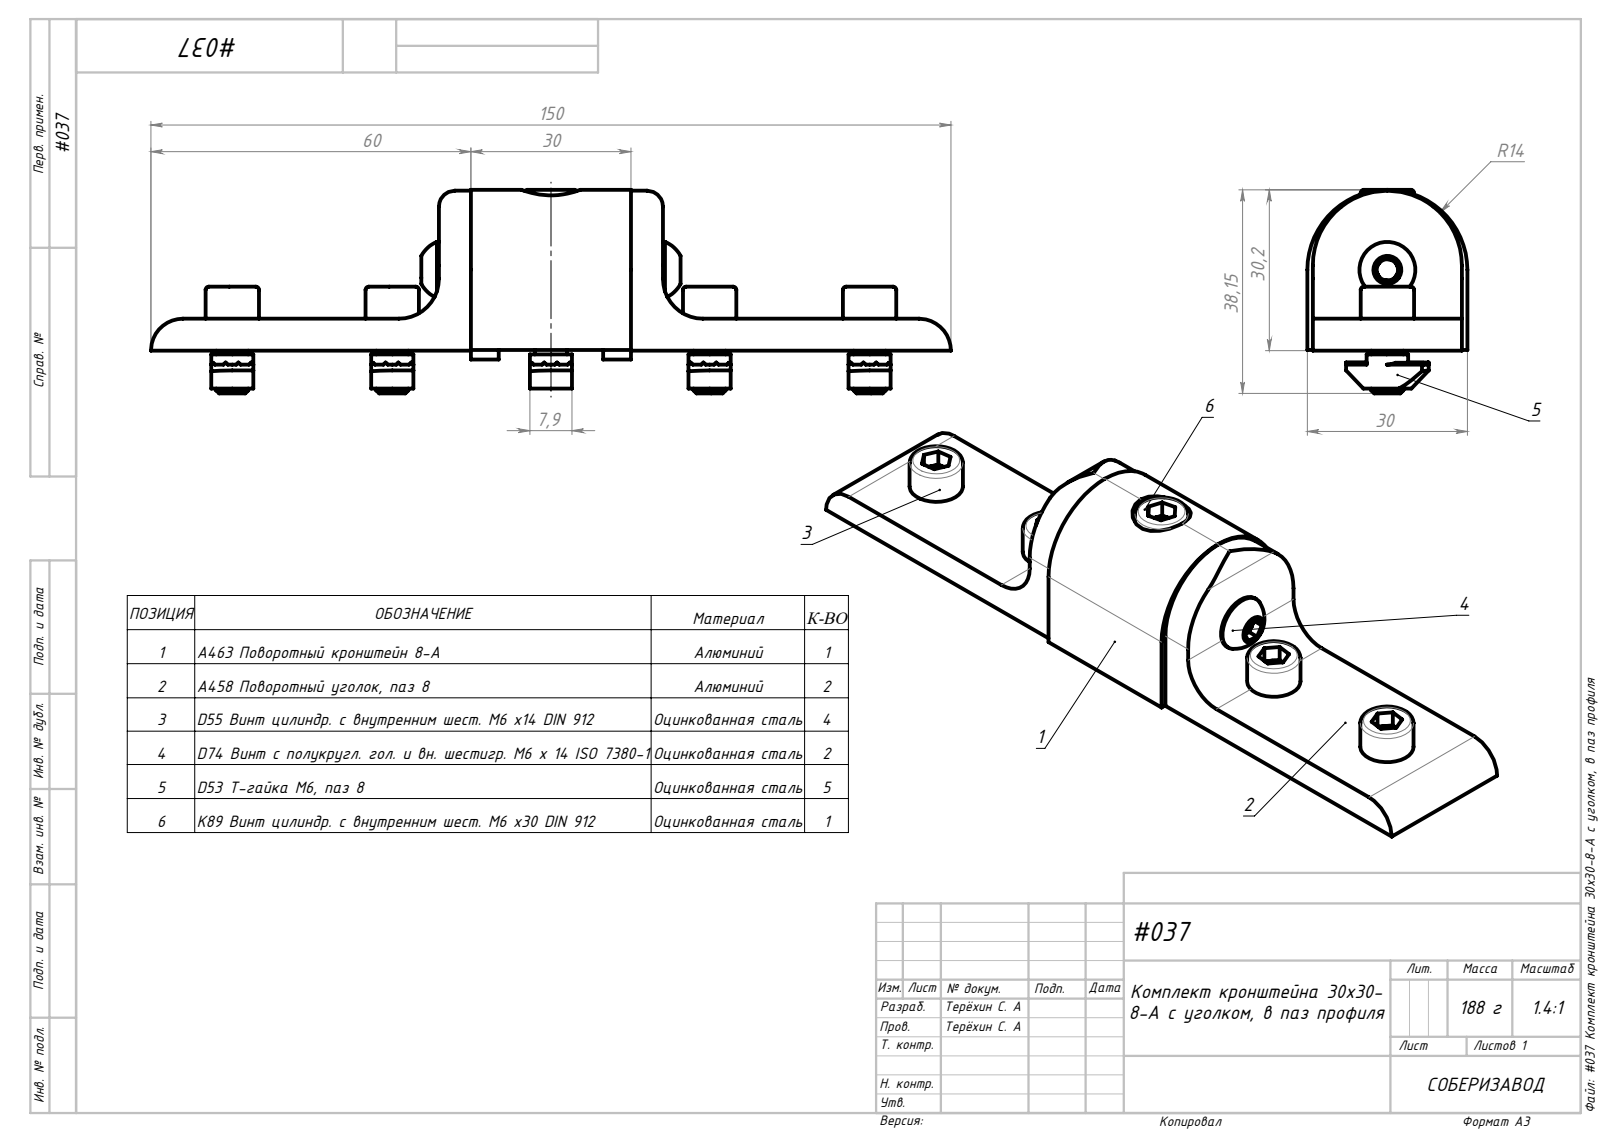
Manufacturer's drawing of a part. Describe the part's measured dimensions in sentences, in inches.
The part is named "A463 Поворотный кронштейн 8-A; #037 Комплект кронштейна 30х30-8-А с уголком, в паз профиля; D74 Винт с полукругл. гол. и вн. шестигр. М6 х 14 ISO 7380-1; D55 Винт цилиндр. с внутренним шест. М6 х14 DIN 912 (+3 more)". Its 3-D file was written by "SolidWorks 2021 (AUTOMOTIVE_DESIGN)". It is 15 solids with 499 faces: 291 planar, 88 cylindrical and 120 other. Overall it measures 5.906 by 1.502 by 1.181 inches. Its volume is 3.43 cubic inches and its surface area 37.88 square inches. Round holes: 5 of diameter 0.197, 5 of diameter 0.248, 1 of diameter 0.201, 1 of diameter 0.262, 1 of diameter 0.433. Round bosses or shafts: 6 of diameter 0.236, 5 of diameter 0.394, 1 of diameter 0.413. Partial cylindrical surfaces (rounded edges, fillets, slot ends): 10 of radius 0.157, 10 of radius 0.27, 2 of radius 0.118, 2 of radius 0.295, 2 of radius 0.551, 1 of radius 0.591. The main face-to-face distances are 0.236, 1.181, 1.1, 0.23, 1.417, 1.141, 0.04, 0.041, 1.141, 1.654. The hole center spacings are 1.171, 1.181, 2.352, 3.524, 2.343, 4.705.
